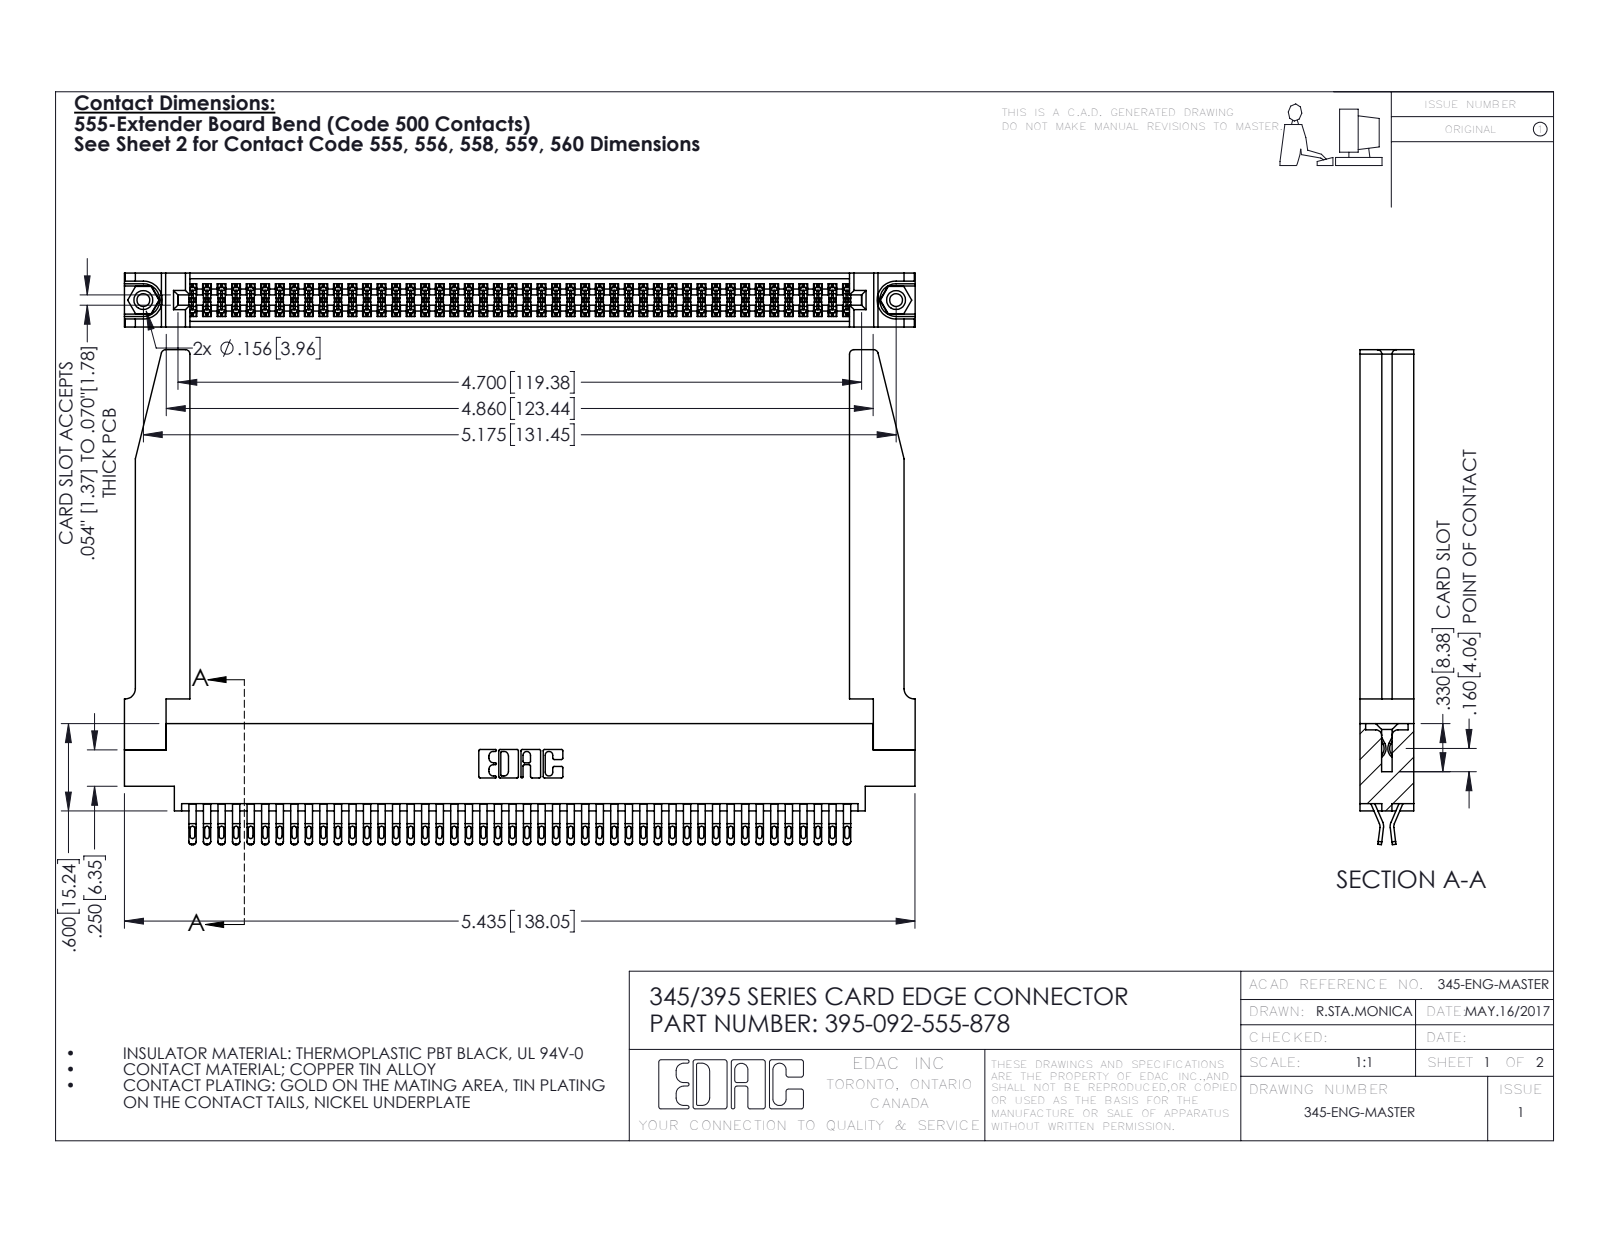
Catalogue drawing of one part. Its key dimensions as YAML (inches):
part_name: "345 Part_0.170 Offset - 0.156 Dia-TH; 345-220-078_345-220-078; 395-092-555-878; 345-250-001_345-250-001-102 (+1 more)"
step_written_by: "SolidWorks 2016 (CONFIG_CONTROL_DESIGN)"
units: inches
bodies: {solids: 97, faces: 5516, planar: 3078, cylindrical: 2386, other: 52}
overall_size: [5.436, 3.402, 0.37]
volume: 1.304
surface_area: 43.55
round_holes:
  - {diameter: 0.089, count: 2}
  - {diameter: 0.125, count: 2}
  - {diameter: 0.156, count: 2}
  - {diameter: 0.064, count: 1}
round_bosses_or_shafts:
  - {diameter: 0.155, count: 2}
partial_cylinders:
  - {radius: 0.016, count: 230}
  - {radius: 0.02, count: 184}
  - {radius: 0.006, count: 138}
  - {radius: 0.01, count: 22}
  - {radius: 0.03, count: 8}
  - {radius: 0.007, count: 6}
  - {radius: 0.031, count: 6}
  - {radius: 0.026, count: 3}
face_to_face_distances: [0.37, 0.072, 0.298, 0.025, 0.2, 0.098, 0.272, 0.225, 0.175, 0.148]
hole_center_spacings: [0.27, 4.939, 5.175]
